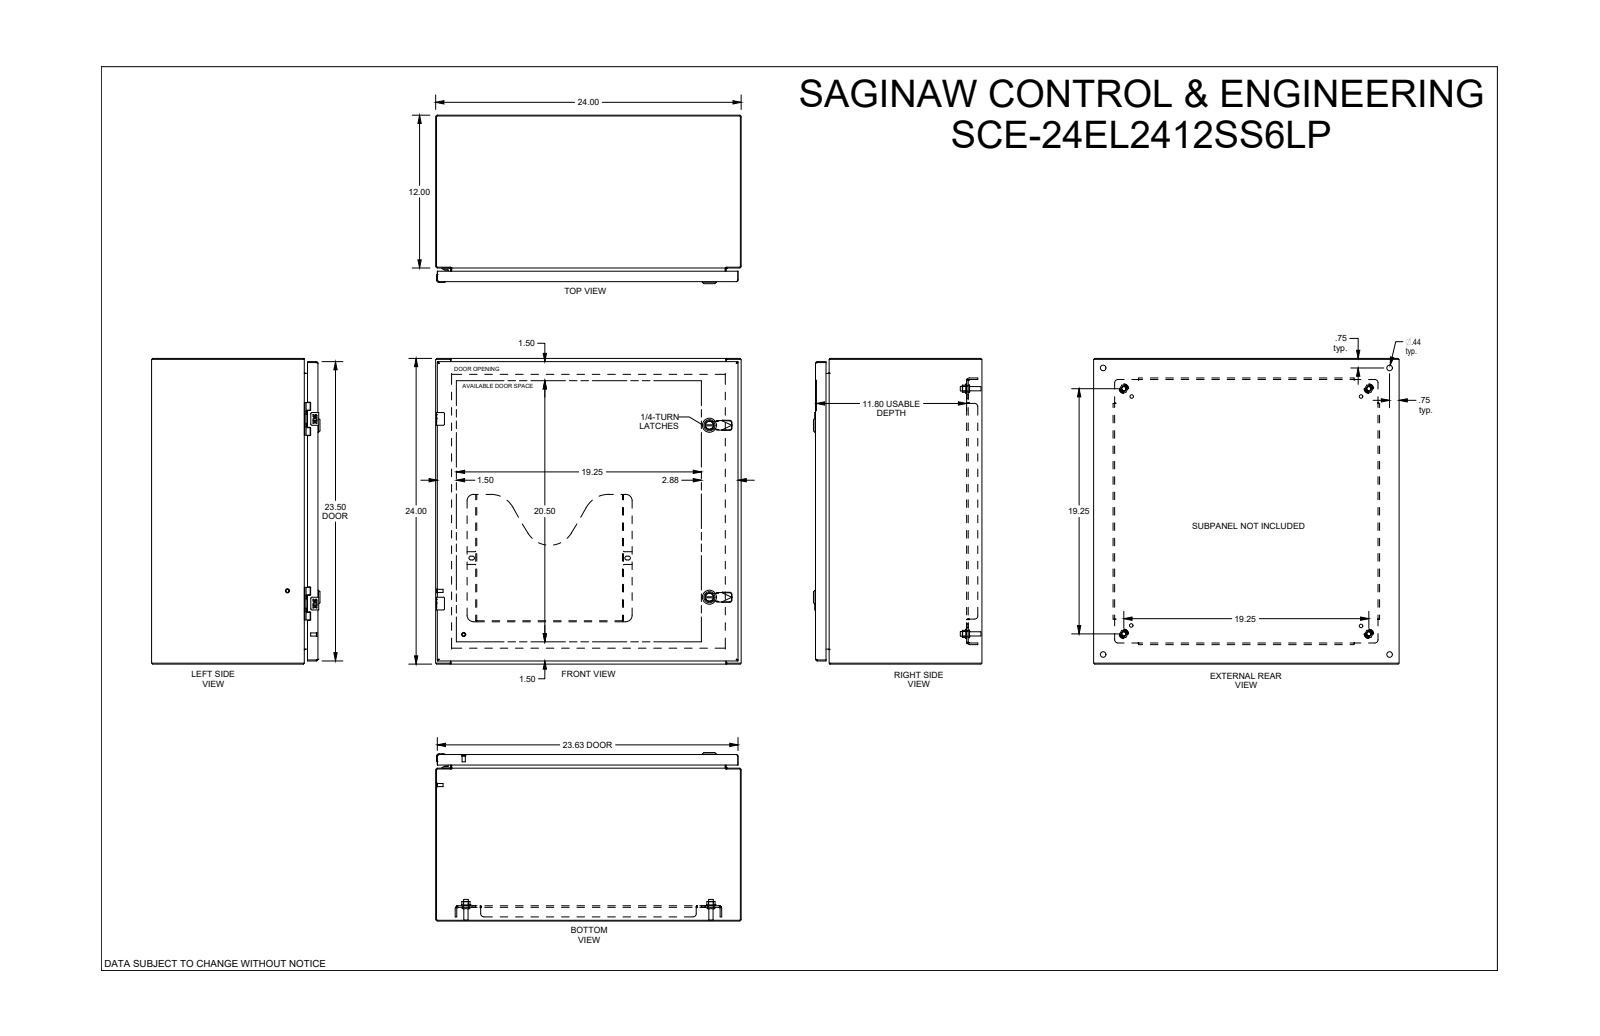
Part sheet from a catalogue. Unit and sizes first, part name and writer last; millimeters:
Units: millimetres
Overall size (bounding box): 609.6 × 609.6 × 336
Round holes (diameter × count): ⌀4.4 ×4, ⌀5.2 ×4, ⌀6.2 ×4, ⌀6.8 ×4, ⌀7.1 ×4, ⌀9.3 ×4, ⌀9.5 ×4, ⌀11.1 ×4, ⌀12.7 ×4, ⌀1 ×2, ⌀4.8 ×2, ⌀5 ×2
Round bosses / shafts (diameter × count): ⌀4.3 ×6, ⌀9.3 ×4, ⌀8.4 ×4, ⌀6.4 ×4, ⌀6.3 ×4, ⌀6.1 ×4, ⌀5 ×3, ⌀28 ×2
Partial cylindrical surfaces — rounded edges, fillets, slot ends (radius × count): R0.3 ×56, R0.3 ×28, R0.4 ×24, R0.5 ×20, R1 ×17, R1.5 ×13, R0.7 ×12, R2.5 ×12
Main face-to-face distances: 1.9, 607.7, 1.5, 605.8, 609.6, 332.1, 330.1, 330.5, 328.6, 30.5
Hole centre spacings: 531.8, 25, 368.3, 473.5, 517.7, 0.5, 12.5, 12.5
Volume: 4 400 000 mm³ · Surface area: 4 217 000 mm²
Bodies: 45 solids, 2819 faces (1099 planar, 850 cylindrical, 870 other)
Part name (STEP PRODUCT): SCE-24EL2412LP
STEP written by: SolidWorks 2021 (AUTOMOTIVE_DESIGN)
